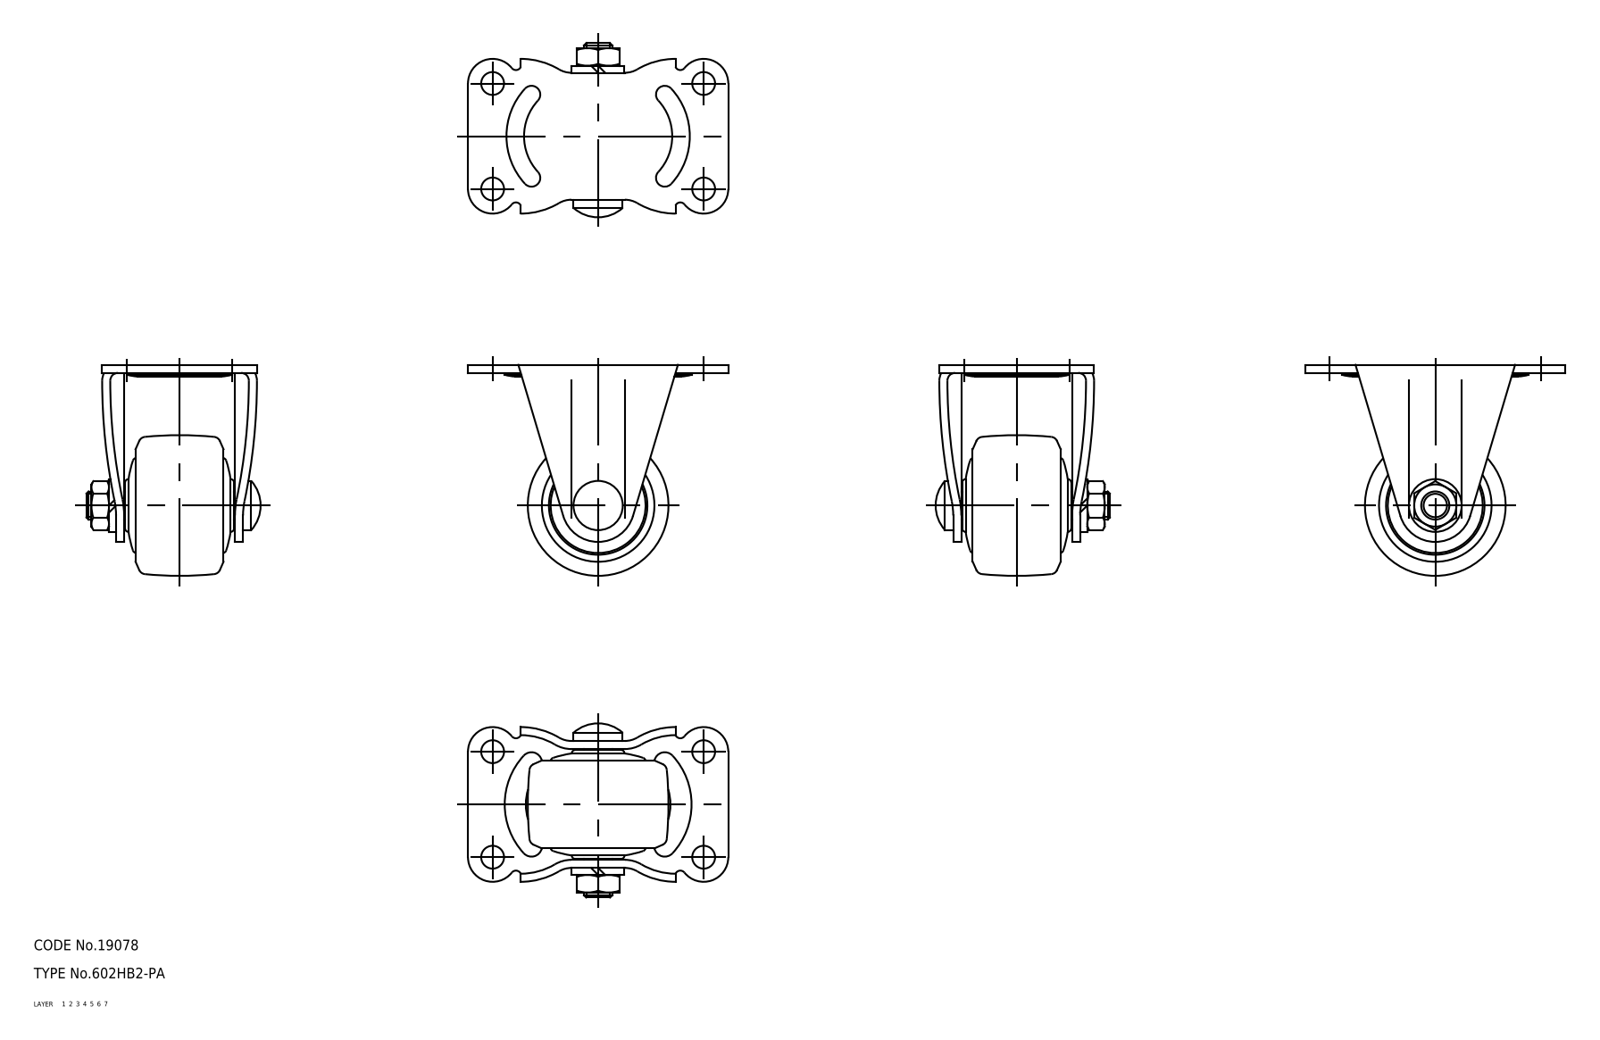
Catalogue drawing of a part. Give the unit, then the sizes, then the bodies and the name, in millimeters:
Units: millimetres
Overall size (bounding box): 74 × 60 × 49.5
Volume: 46 236 mm³ · Surface area: 21 271 mm²
Bodies: 3 solids, 191 faces (0 planar, 0 cylindrical, 191 other)
Part name (STEP PRODUCT): wheel; axle; No_602HB2_PA_13882_36
STEP written by: CADfix (AUTOMOTIVE_DESIGN)
